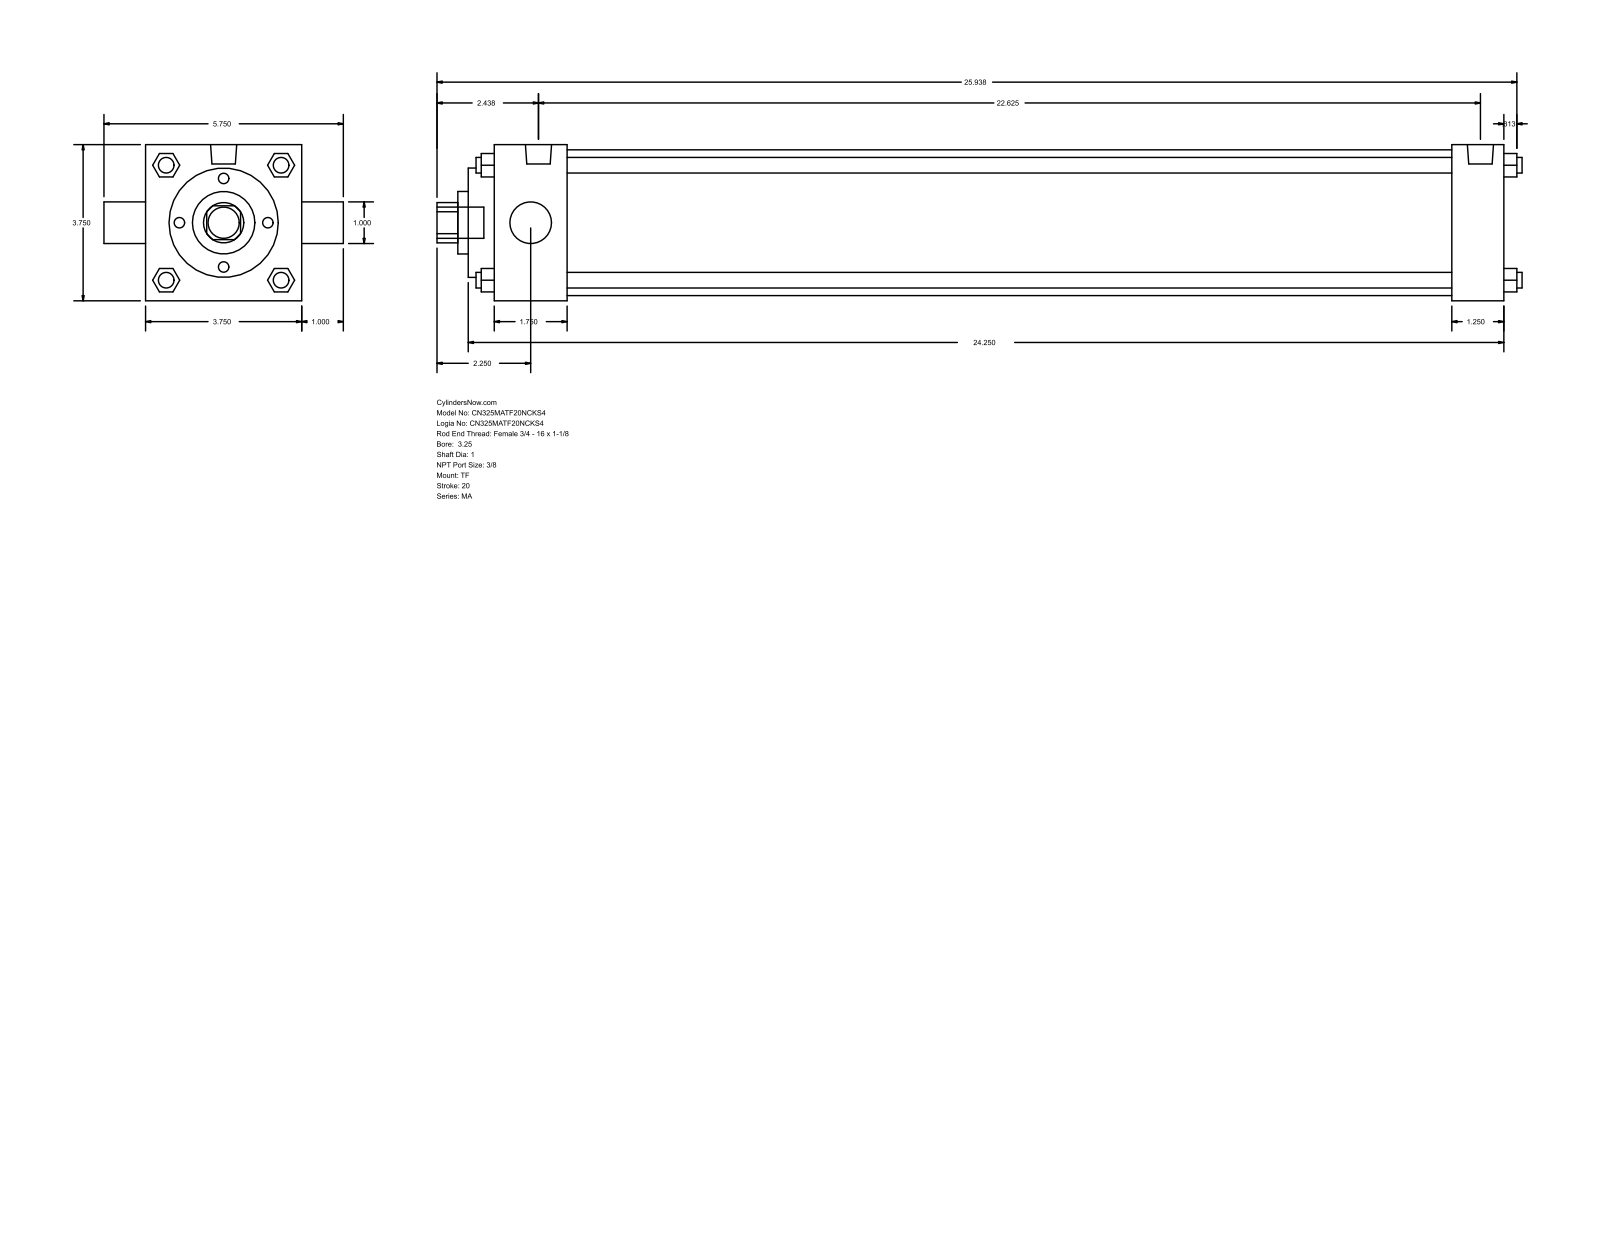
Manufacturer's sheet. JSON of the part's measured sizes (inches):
{"part_name": "MA_TF__0325_1", "step_written_by": "GSSL Pune (CONFIG_CONTROL_DESIGN)", "units": "inches", "bodies": {"solids": 0, "faces": 122, "planar": 93, "cylindrical": 29, "other": 0}, "overall_size": [26.063, 5.75, 3.75], "round_holes": [[1, 2], [1.5, 1], [2.625, 1], [3.5, 1]], "round_bosses_or_shafts": [[0.375, 4], [0.437, 3], [0.627, 2], [0.75, 1]], "partial_cylinders_radius": [[0.484, 1]], "face_to_face_distances": [3.75, 24.25, 0.625, 1.75, 23, 21.25, 22.5, 1.25, 2.375, 23.625]}
